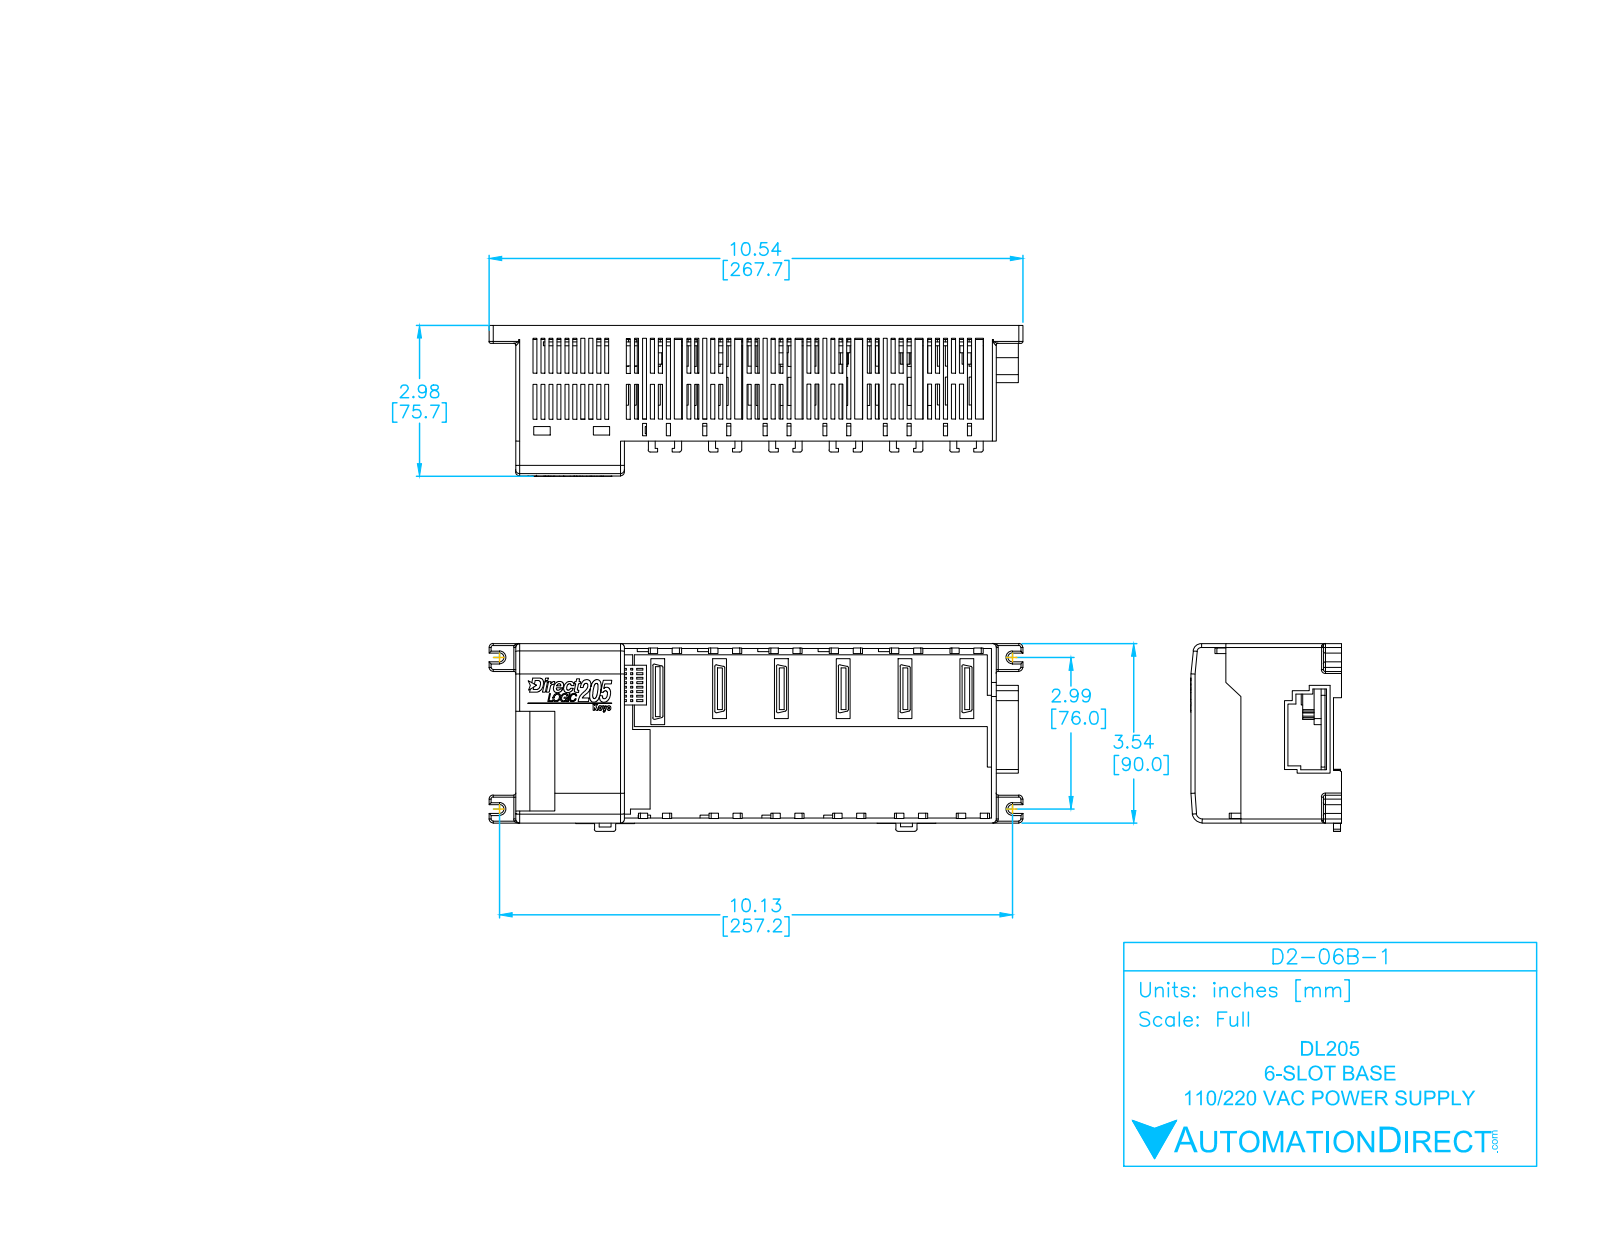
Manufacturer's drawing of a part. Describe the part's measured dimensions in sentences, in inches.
The part is named "D2-06B-1". Its 3-D file was written by "SolidWorks 2009 (AUTOMOTIVE_DESIGN)". It is 6 solids with 2240 faces: 1903 planar, 174 cylindrical and 163 other. Overall it measures 10.538 by 3.709 by 2.98 inches. Its volume is 17.67 cubic inches and its surface area 297 square inches. Round bosses or shafts: 6 of diameter 0.213. Partial cylindrical surfaces (rounded edges, fillets, slot ends): 64 of radius 0.039, 24 of radius 0.03, 20 of radius 0.079, 16 of radius 0.01, 4 of radius 0.087, 4 of radius 0.185, 1 of radius 0.162, 1 of radius 0.208. The main face-to-face distances are 0.098, 0.118, 0.049, 3.346, 3.445, 0.079, 0.167, 0.246, 0.128, 3.543.
